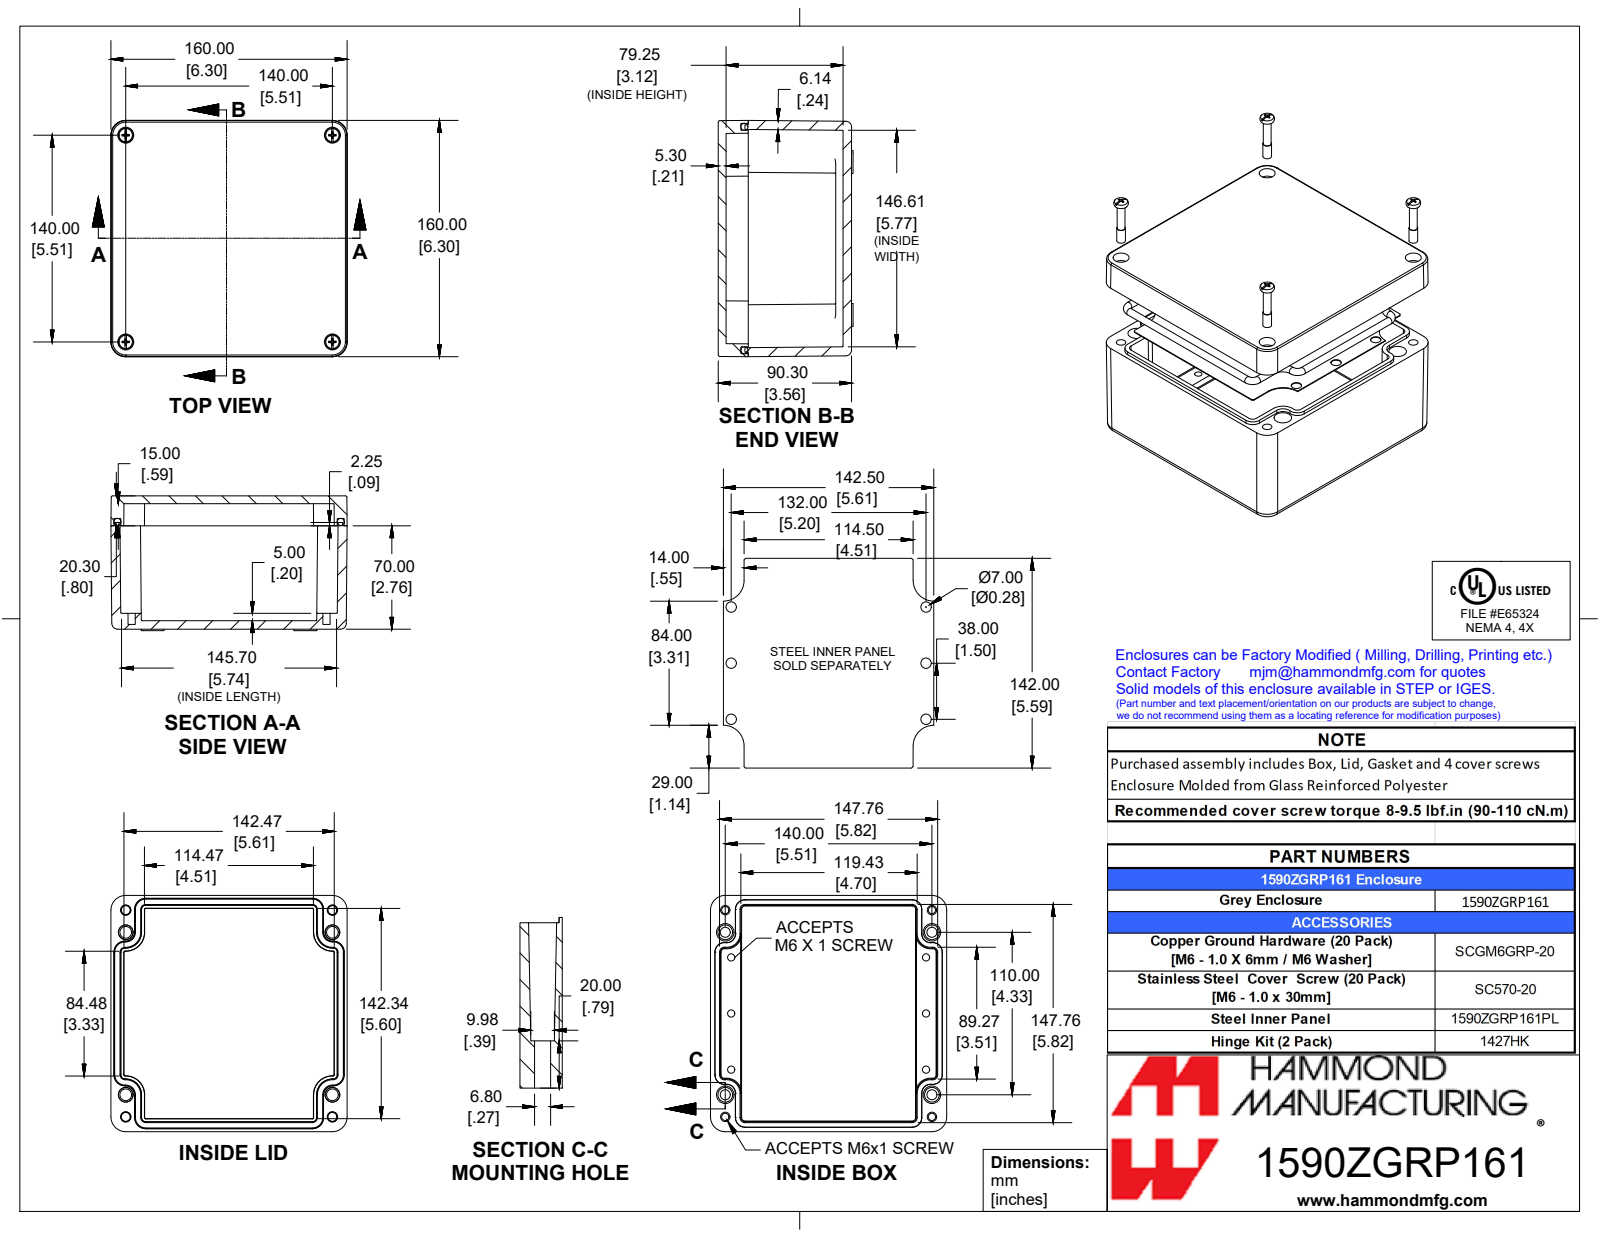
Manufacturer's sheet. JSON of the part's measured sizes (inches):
{"part_name": "1590ZGRP161", "step_written_by": "SolidWorks 2019 (CONFIG_CONTROL_DESIGN)", "units": "inches", "bodies": {"solids": 8, "faces": 483, "planar": 225, "cylindrical": 98, "other": 160}, "overall_size": [6.299, 6.299, 3.594], "volume_in3": 43.5, "surface_area_in2": 418.4, "round_holes": [[0.194, 10], [0.276, 6], [0.236, 4], [0.252, 4], [0.268, 4], [0.425, 4]], "round_bosses_or_shafts": [[0.189, 6], [0.231, 4], [0.208, 4]], "partial_cylinders_radius": [[0.02, 18], [0.059, 8], [0.394, 8], [0.039, 4], [0.157, 4], [0.551, 4]], "face_to_face_distances": [0.242, 3.555, 0.423, 3.132, 0.197, 3.346, 2.923, 0.209, 0.02, 0.443], "hole_center_spacings": [5.512, 0.591, 0.687, 1.27, 1.496, 2.171, 2.76, 3.665]}
